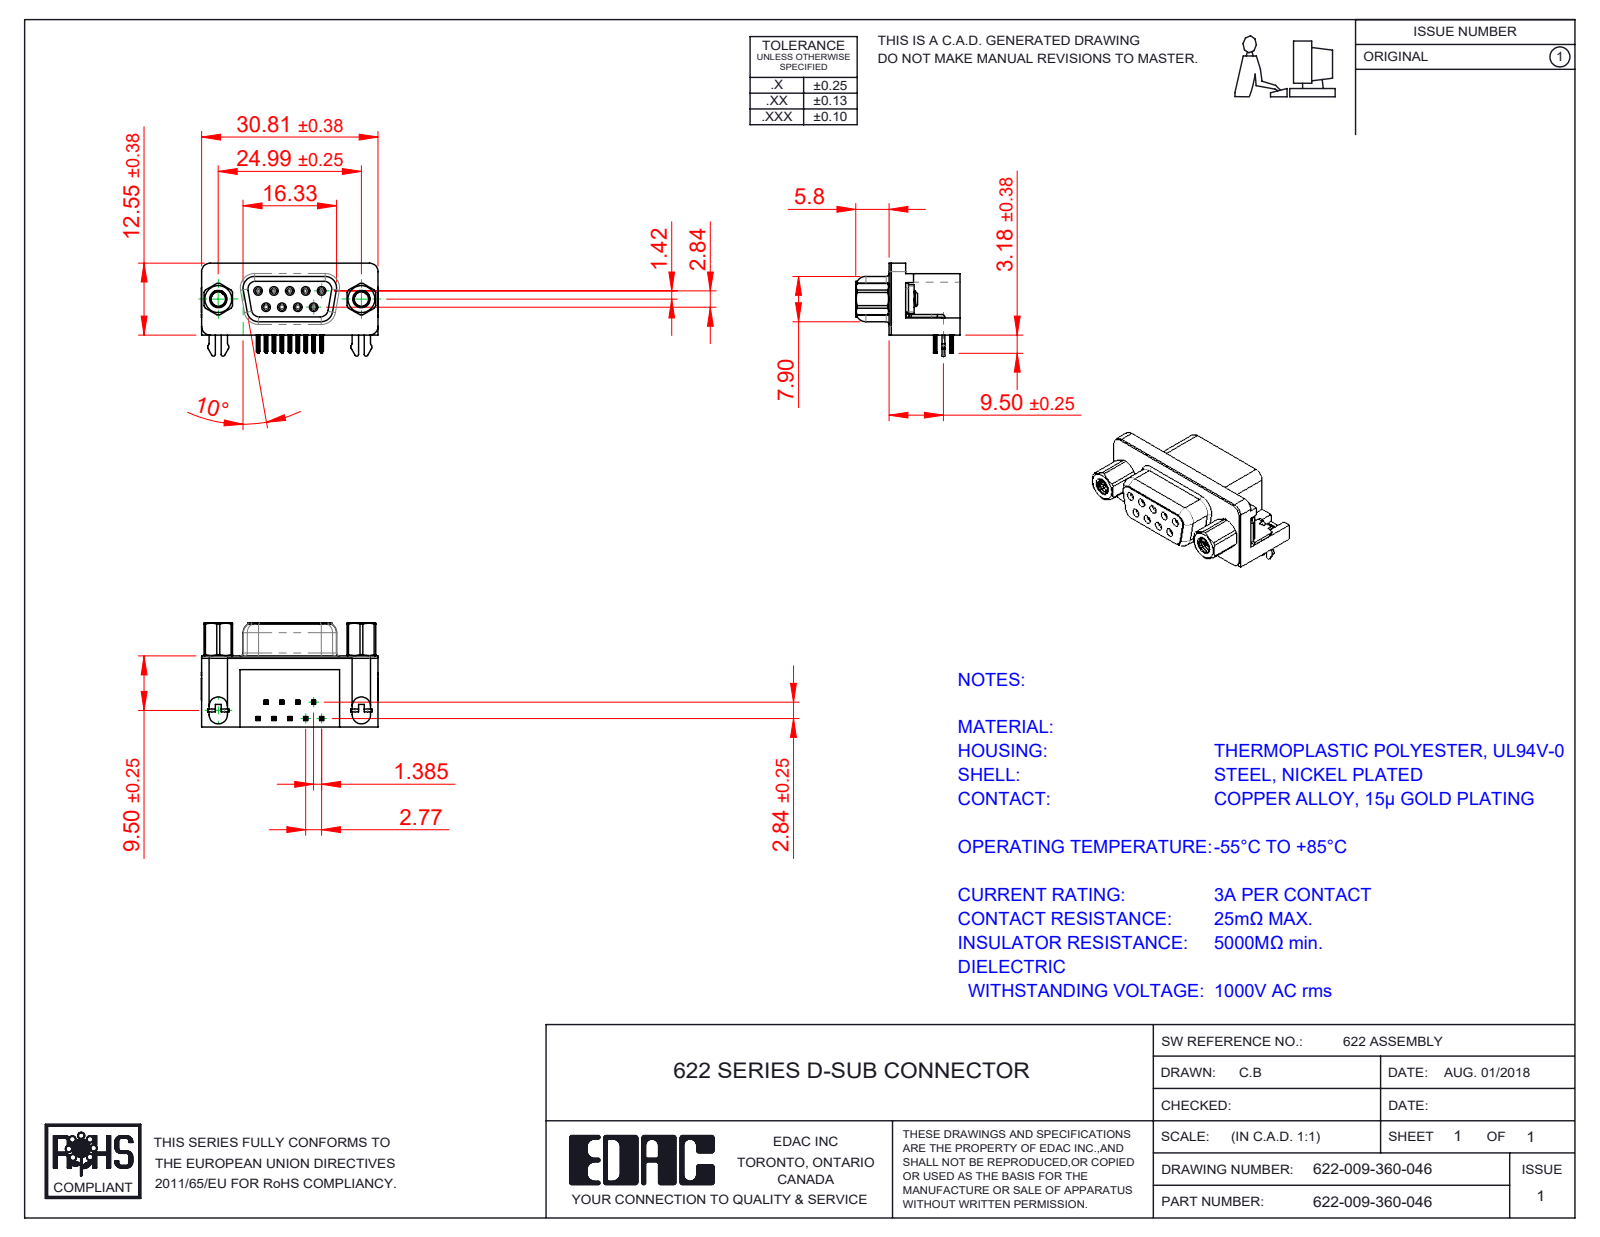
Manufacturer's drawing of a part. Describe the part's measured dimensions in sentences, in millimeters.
The part is named "622 Housing_9 Socket; 622 4 Prong Board Lock; 622 Contact Top; 622-009-360-046 (+3 more)". Its 3-D file was written by "SolidWorks 2016 (CONFIG_CONTROL_DESIGN)". It is 15 solids with 1692 faces: 726 planar, 426 cylindrical and 540 other. Overall it measures 30.89 by 18.2 by 16.25 millimeters. Its volume is 3 730 cubic millimeters and its surface area 5 151 square millimeters. Round holes: 9 of diameter 0.8, 9 of diameter 0.9, 2 of diameter 2, 2 of diameter 2.5, 2 of diameter 4, 2 of diameter 4.8, 2 of diameter 5. Round bosses or shafts: 9 of diameter 1.2, 2 of diameter 4.9, 2 of diameter 4.75, 2 of diameter 3.9, 2 of diameter 3. Partial cylindrical surfaces (rounded edges, fillets, slot ends): 72 of radius 0.1, 36 of radius 0.15, 18 of radius 0.35, 18 of radius 1, 12 of radius 0.25, 9 of radius 0.34, 8 of radius 1.35, 8 of radius 1.6. The main face-to-face distances are 0.4, 12, 12.4, 0.35, 2.9, 2.5, 6.2, 10.34, 9.5, 5.8. The hole center spacings are 3.16, 2.77, 5.54, 5.03, 5.04, 8.31, 7.48, 7.49.
